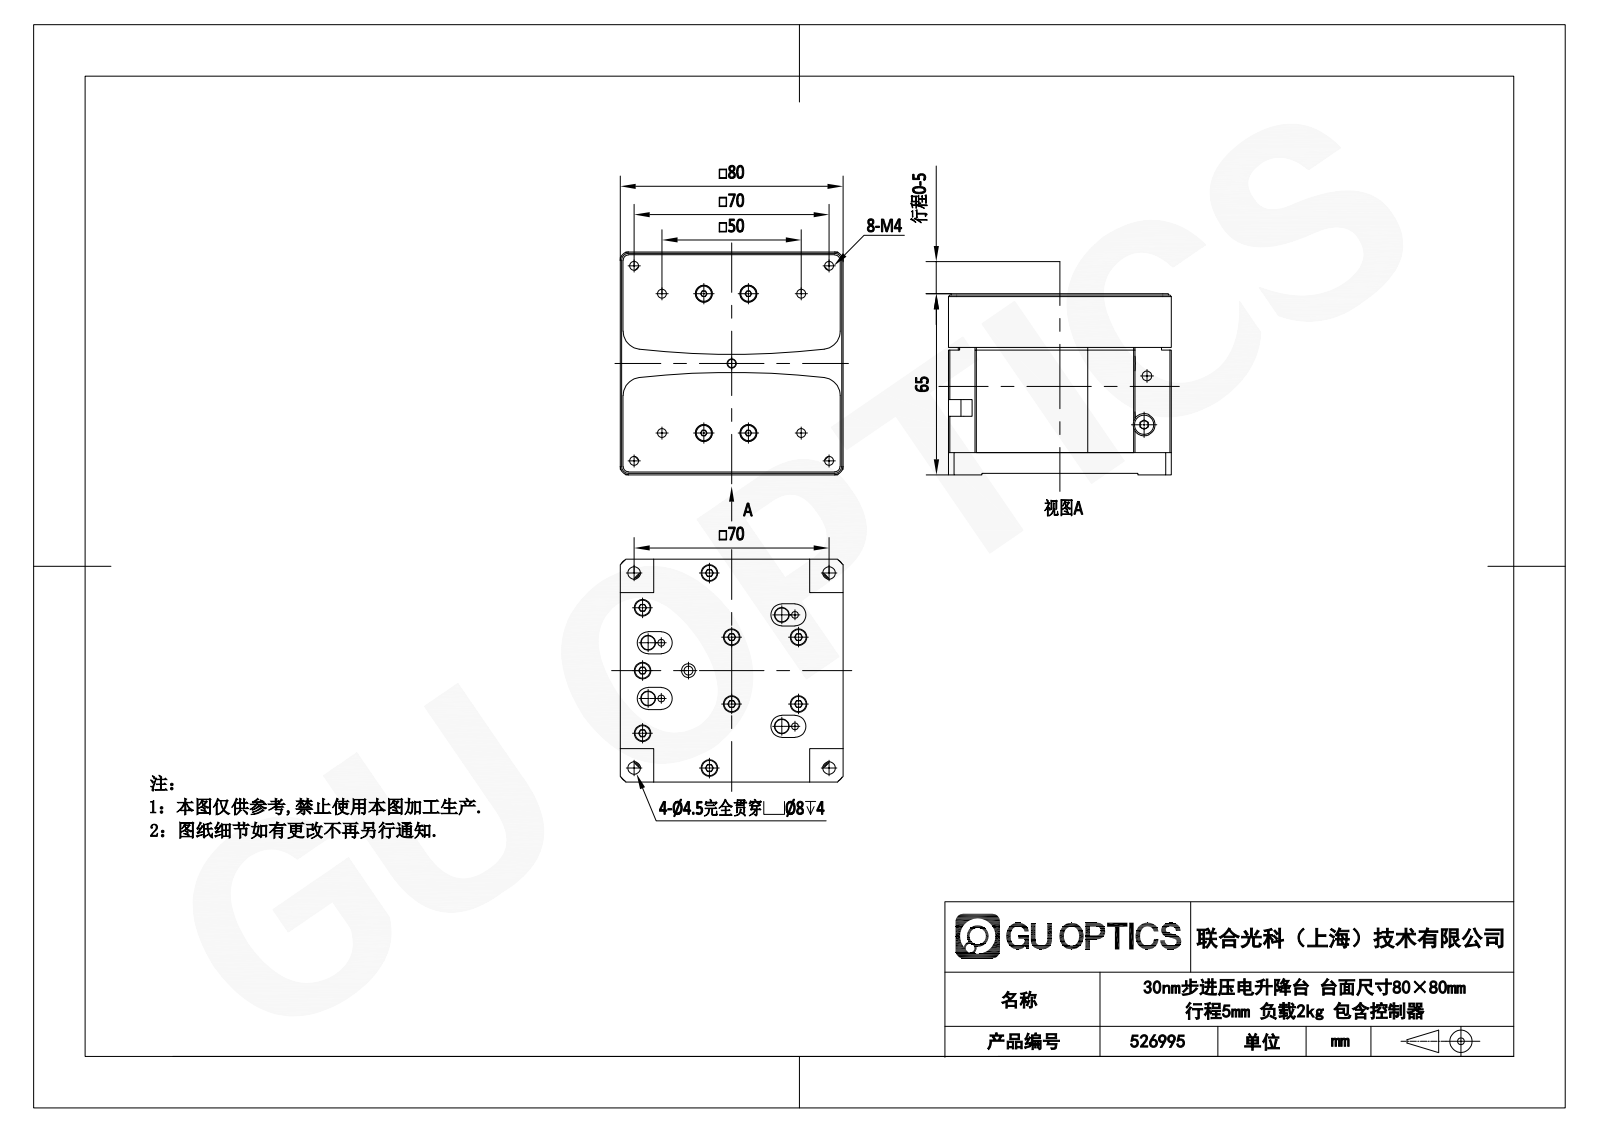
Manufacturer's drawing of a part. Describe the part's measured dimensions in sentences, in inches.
The part is named "socket head cap screw_din_DIN 912 M3 x 5 --- 5N; 526964; socket head cap screw_din_DIN 912 M2 x 3 --- 3N; socket head cap screw_din_DIN 912 M4 x 6 --- 6N (+1 more)". Its 3-D file was written by "SolidWorks 2020 (CONFIG_CONTROL_DESIGN)". It is 37 solids with 1804 faces: 834 planar, 613 cylindrical and 357 other. Overall it measures 3.15 by 3.15 by 2.559 inches. Its volume is 19.64 cubic inches and its surface area 188.4 square inches. Round holes: 23 of diameter 0.098, 21 of diameter 0.134, 20 of diameter 0.177, 17 of diameter 0.236, 16 of diameter 0.13, 16 of diameter 0.315, 8 of diameter 0.118, 8 of diameter 0.244, 7 of diameter 0.138, 4 of diameter 0.049, 4 of diameter 0.063, 4 of diameter 0.094. Round bosses or shafts: 28 of diameter 0.118, 9 of diameter 0.217, 7 of diameter 0.276, 7 of diameter 0.157, 5 of diameter 0.218, 4 of diameter 0.272, 4 of diameter 0.15, 4 of diameter 0.079. Partial cylindrical surfaces (rounded edges, fillets, slot ends): 27 of radius 0.157, 19 of radius 0.079, 10 of radius 0.059, 7 of radius 0.118, 6 of radius 0.039, 4 of radius 0.02, 4 of radius 0.256, 4 of radius 0.394. The main face-to-face distances are 0.02, 3.15, 1.969, 2.303, 0.236, 0.295, 2.539, 0.335, 2.008, 1.24. The hole center spacings are 0.984, 2.756, 0.394, 1.815, 0.512, 1.282, 0.127, 0.185.
